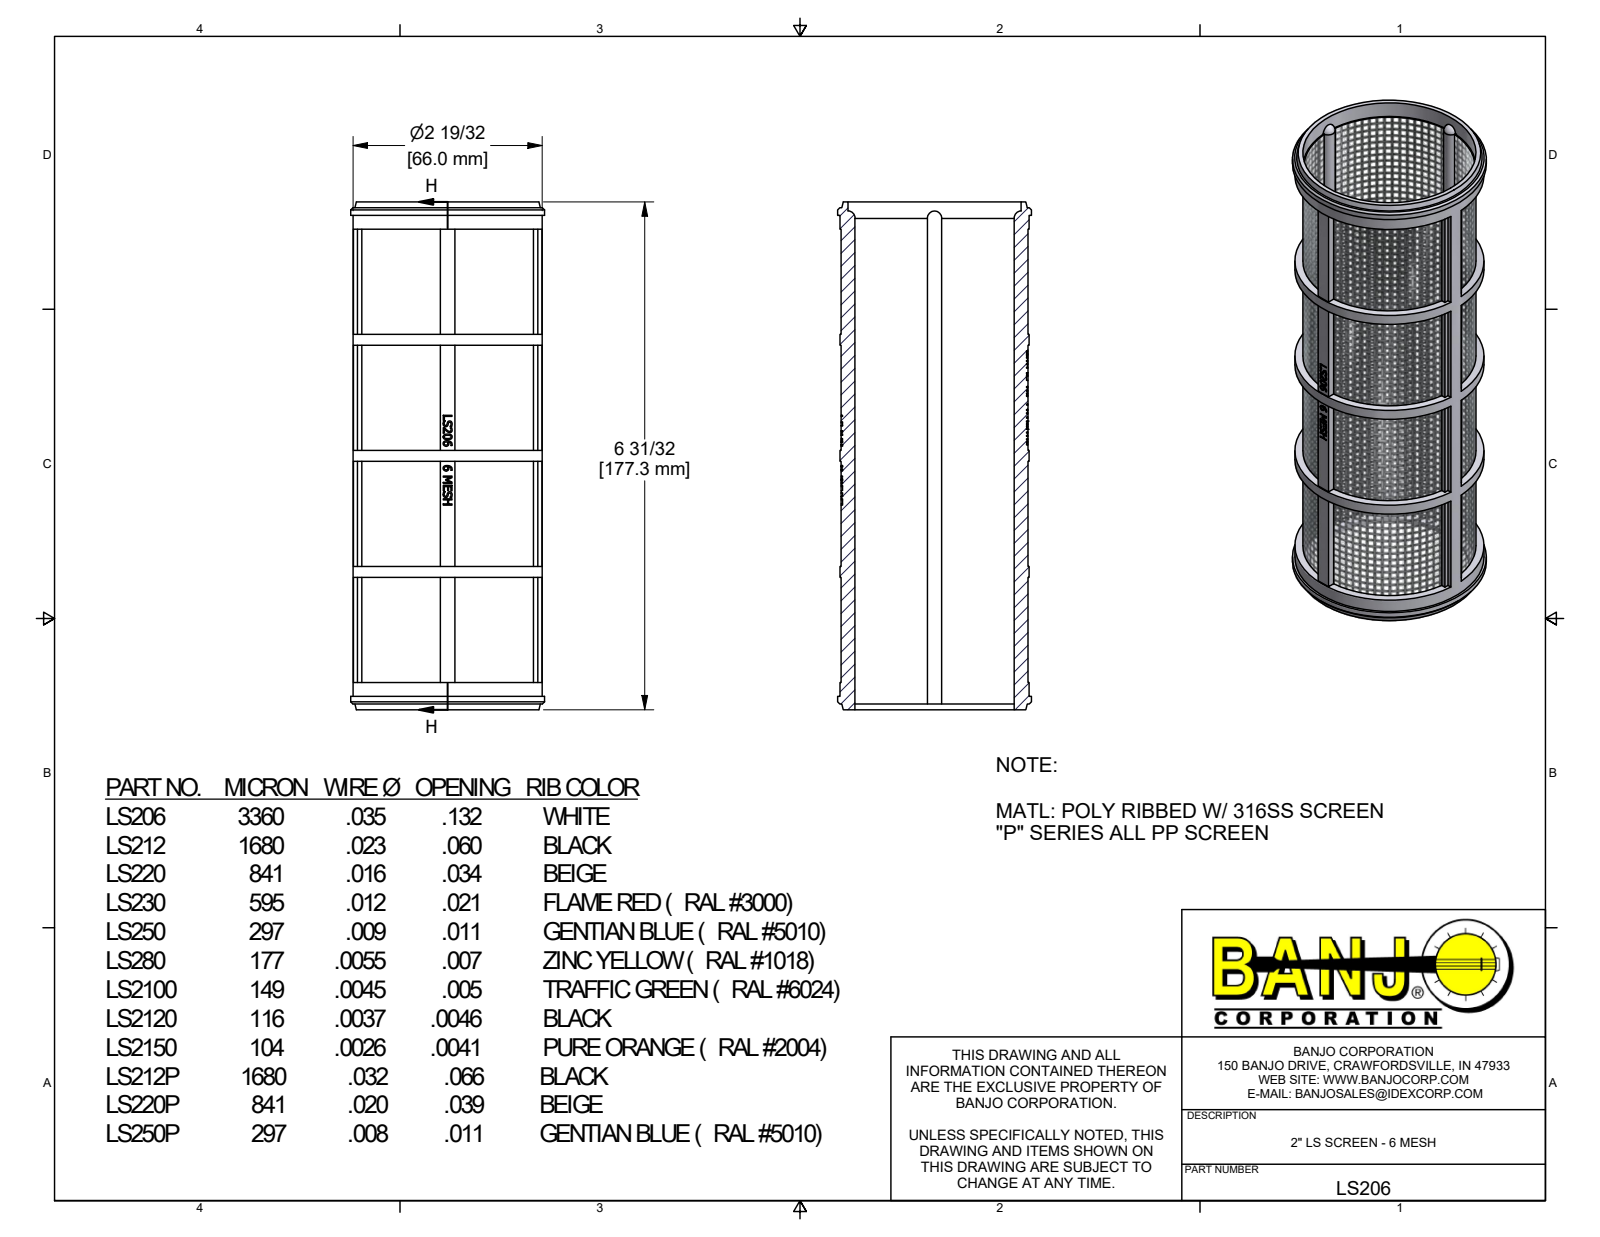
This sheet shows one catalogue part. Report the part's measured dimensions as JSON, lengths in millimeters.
{"part_name": "LS206", "step_written_by": "Autodesk Inventor 2019 (AUTOMOTIVE_DESIGN)", "units": "millimeters", "bodies": {"solids": 1, "faces": 459, "planar": 321, "cylindrical": 29, "other": 109}, "overall_size": [177.3, 67.7, 67.7], "volume_mm3": 44260, "surface_area_mm2": 78320, "round_holes": [[55.6, 1], [59.7, 1]], "round_bosses_or_shafts": [[67.7, 1], [66, 1], [60.5, 1]], "partial_cylinders_radius": [[2.5, 4]], "face_to_face_distances": [40.5, 36.7, 3.8, 5.1, 81, 40.5, 81, 121.5, 36.7, 77.2]}
